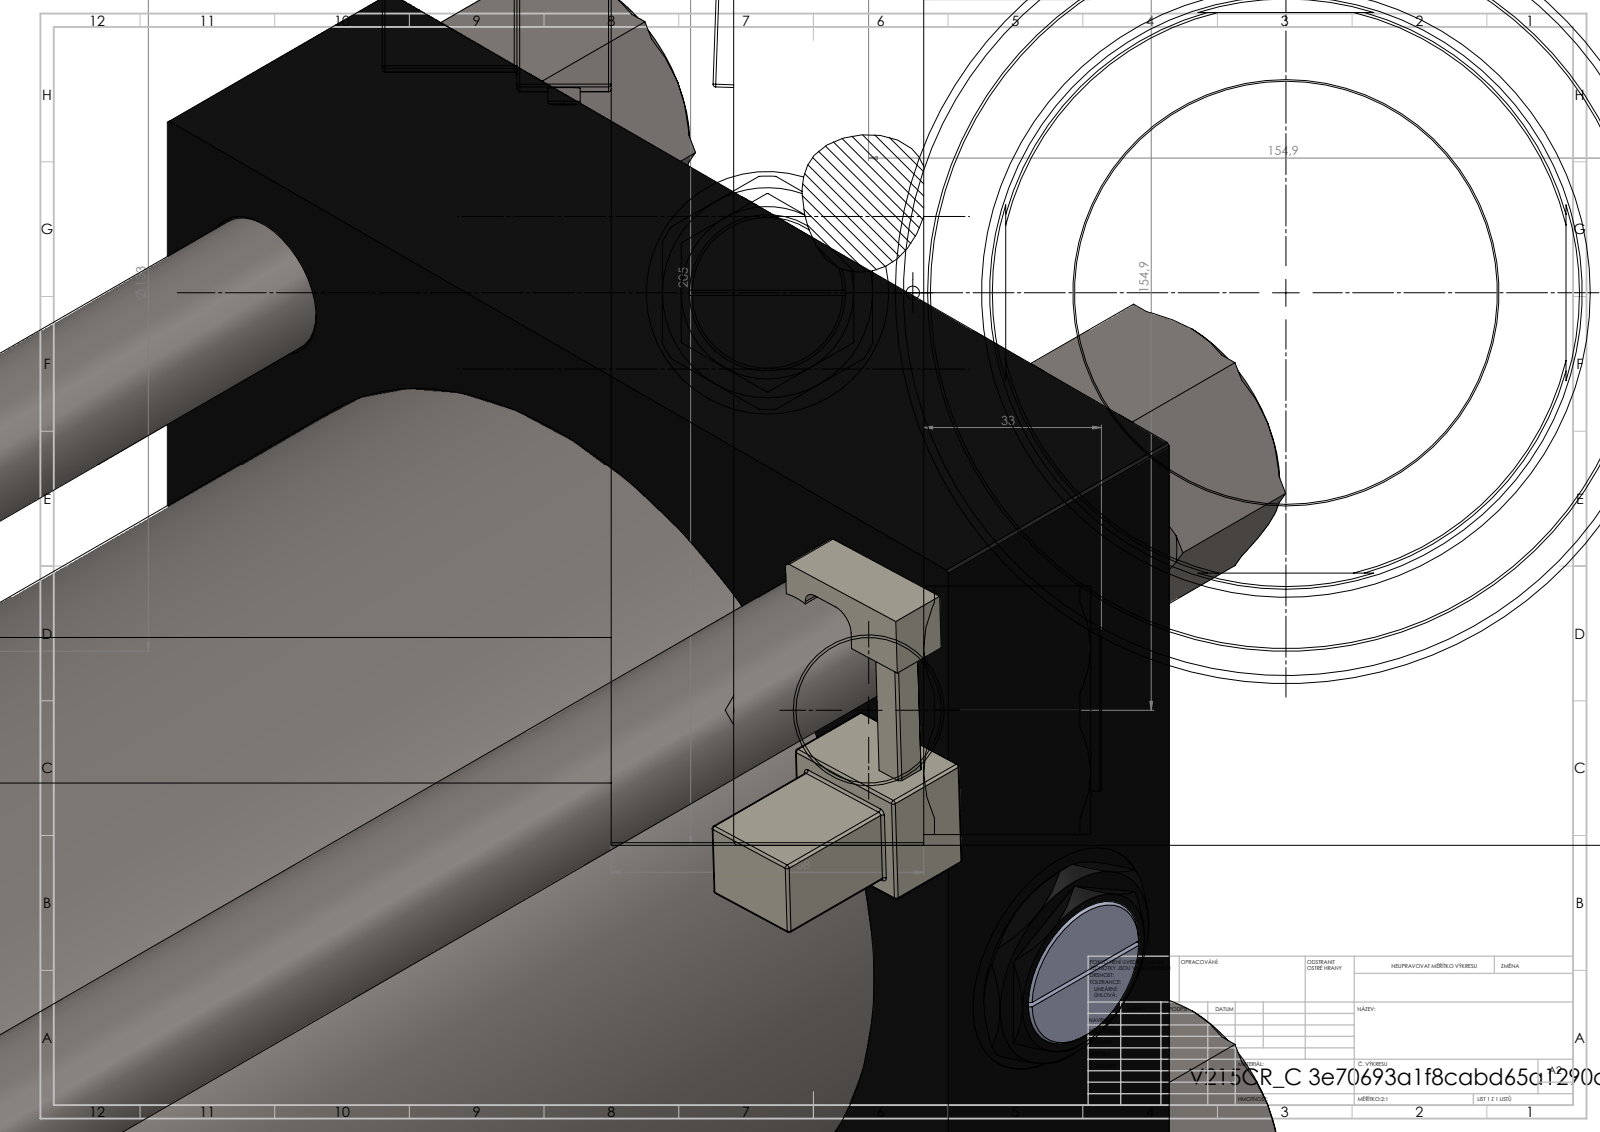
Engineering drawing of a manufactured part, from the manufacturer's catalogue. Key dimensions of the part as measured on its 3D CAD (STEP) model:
Part name (STEP PRODUCT): V215CR_MSU; V215_VC_A; NUT_M5_C; Zatka_pro_OIL_PORT (+3 more)
STEP written by: SolidWorks 2019 (CONFIG_CONTROL_DESIGN)
Units: millimetres
Bodies: 14 solids, 1410 faces (658 planar, 158 cylindrical, 594 other)
Overall size (bounding box): 526 × 215.84 × 205
Volume: 10 750 000 mm³ · Surface area: 1 133 000 mm²
Round holes (diameter × count): ⌀27 ×4, ⌀2.5 ×2, ⌀7 ×2, ⌀33.24 ×2, ⌀45 ×2, ⌀78.5 ×1, ⌀110 ×1, ⌀113 ×1, ⌀120 ×1, ⌀142 ×1, ⌀160 ×1
Round bosses / shafts (diameter × count): ⌀30 ×4, ⌀6 ×2, ⌀166 ×1, ⌀133 ×1
Partial cylindrical surfaces — rounded edges, fillets, slot ends (radius × count): R0.5 ×48, R1 ×2, R2.5 ×2, R4 ×2, R54 ×1
Main face-to-face distances: 205, 58, 380, 322, 461, 403, 81, 130, 432.3, 374.3
Hole centre spacings: 77.88, 109.53, 154.9, 165.89, 69.25, 219.06, 138.5, 378
